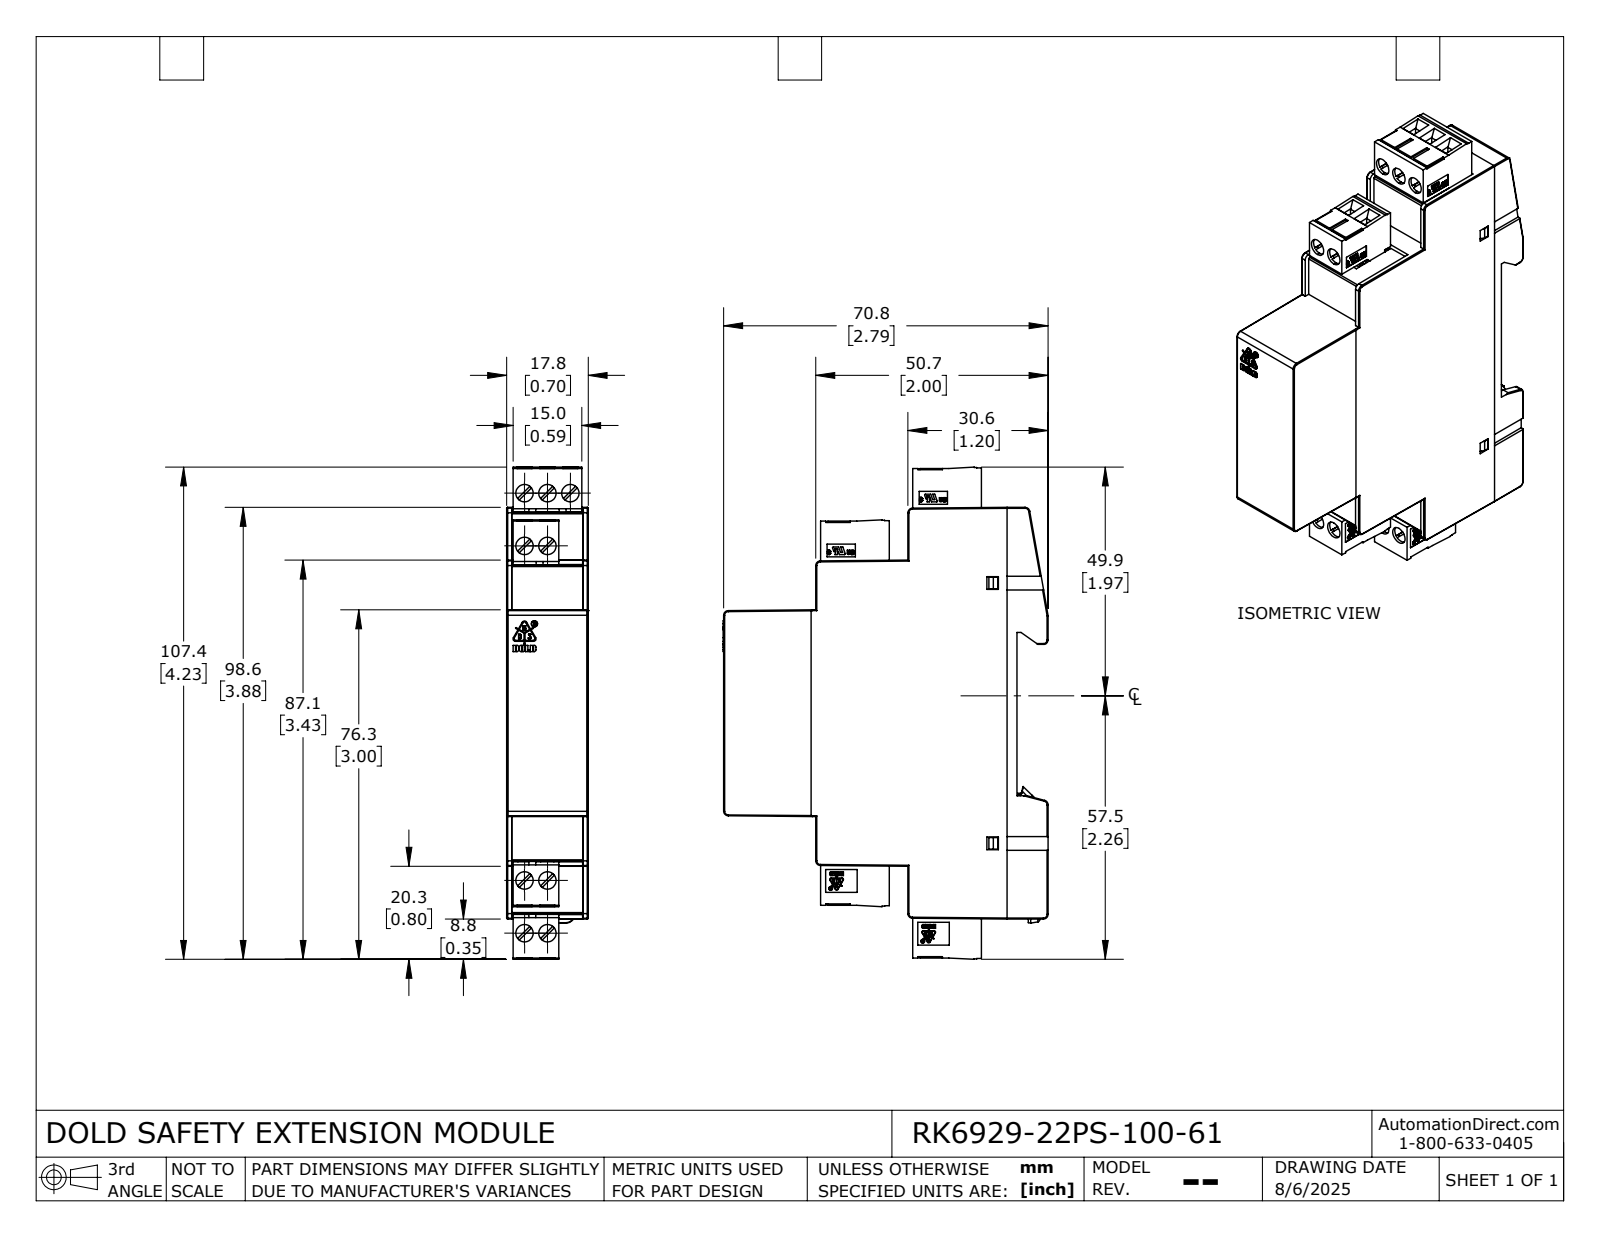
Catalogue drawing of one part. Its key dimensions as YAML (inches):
part_name: "PS_00_RK6929_Step"
step_written_by: "SolidWorks 2024 (AUTOMOTIVE_DESIGN)"
units: inches
bodies: {solids: 1, faces: 2429, planar: 1857, cylindrical: 491, other: 81}
overall_size: [4.228, 2.791, 0.701]
volume: 5.198
surface_area: 37.9
round_holes:
  - {diameter: 0.15, count: 9}
  - {diameter: 0.138, count: 5}
  - {diameter: 0.03, count: 4}
  - {diameter: 0.05, count: 1}
round_bosses_or_shafts:
  - {diameter: 0.032, count: 4}
  - {diameter: 0.054, count: 1}
partial_cylinders:
  - {radius: 0.008, count: 42}
  - {radius: 0.01, count: 40}
  - {radius: 0.02, count: 23}
  - {radius: 0.039, count: 13}
  - {radius: 0.004, count: 9}
  - {radius: 0.012, count: 9}
  - {radius: 0.005, count: 8}
  - {radius: 0.007, count: 8}
face_to_face_distances: [0.701, 0.791, 0.646, 0.055, 2.52, 0.589, 0.36, 0.449, 0.394, 0.252]
hole_center_spacings: [0.197, 0.494, 3.333, 0.453, 3.327, 0.815, 3.785, 0.394]
